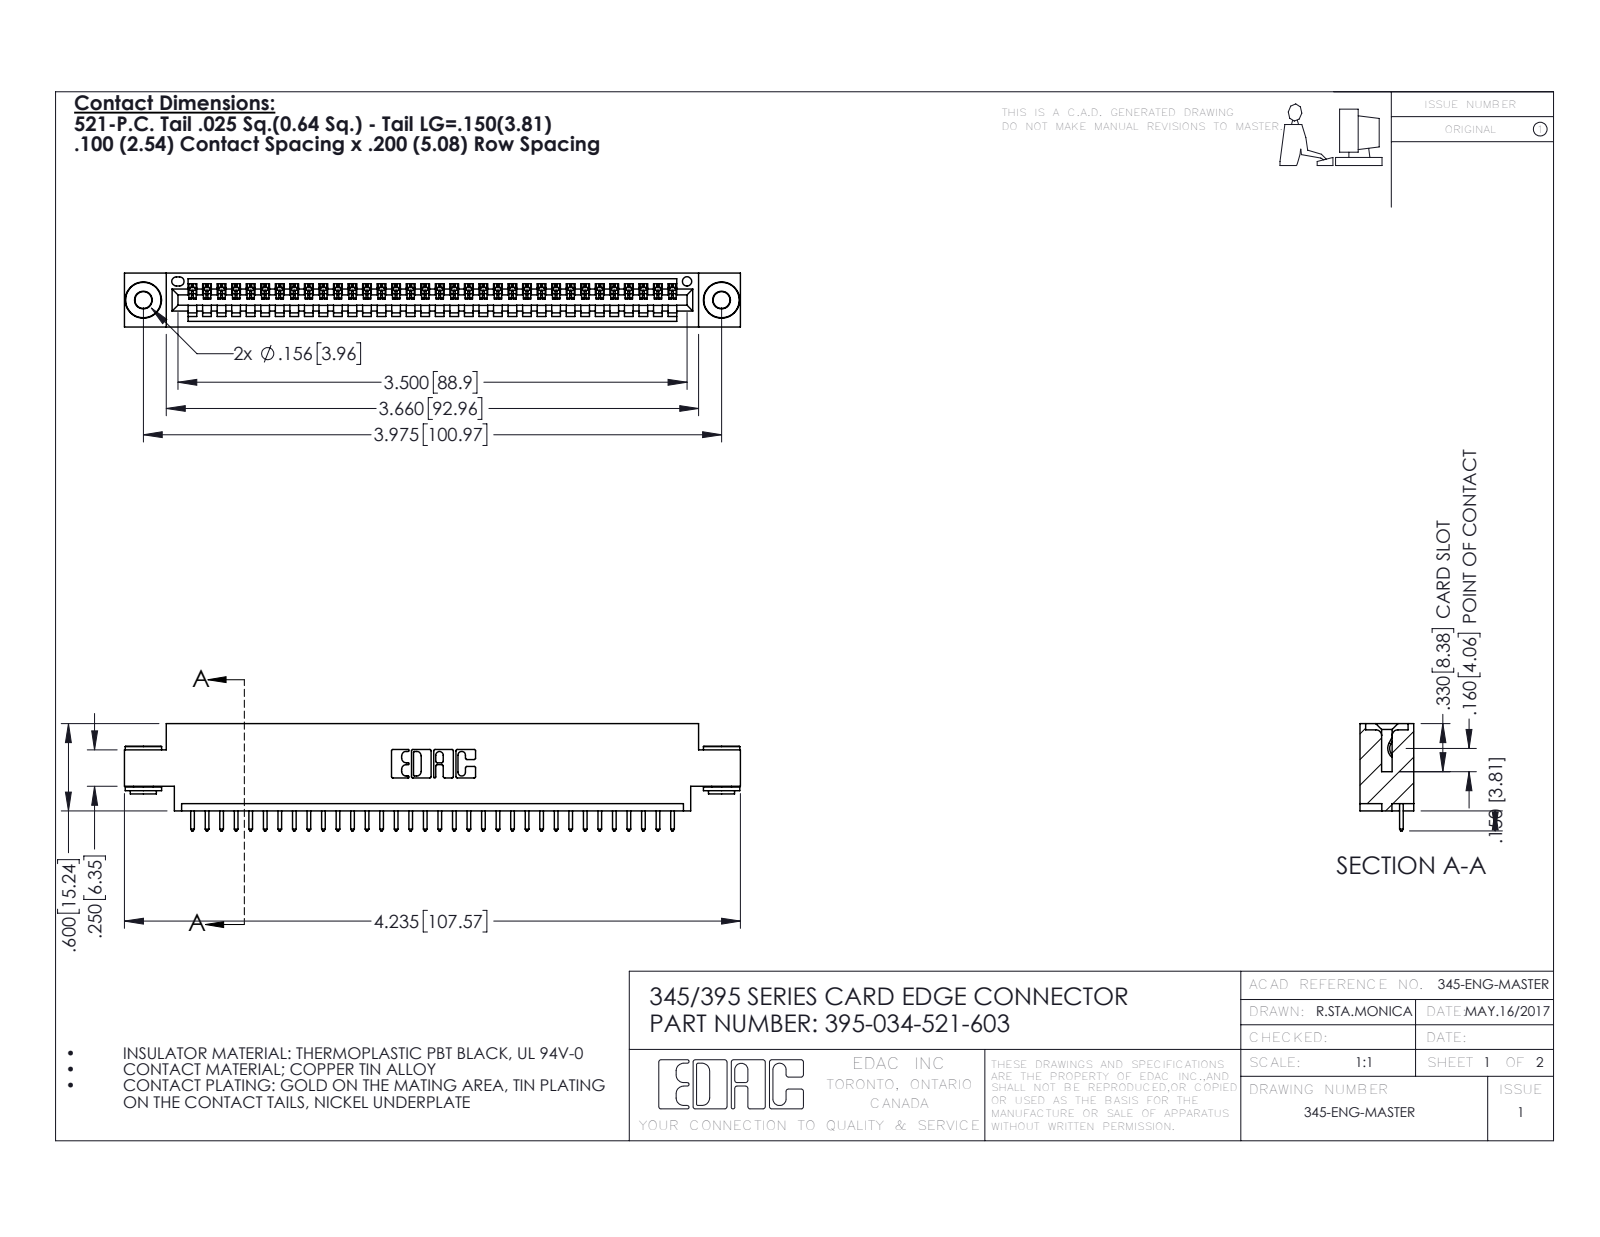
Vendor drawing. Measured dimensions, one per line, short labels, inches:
name: 345-250-002_345-250-002-102; 345-292-001_345-293-121; 395-034-521-603; 345 Part_0.170 Offset - 0.156 Dia-TH
written by: SolidWorks 2016 (CONFIG_CONTROL_DESIGN)
unit: in
bodies: 37 solids, 2140 faces (1454 planar, 678 cylindrical, 8 other)
size: 4.235 × 0.737 × 0.37
volume: 0.608 in³; area: 20.29 in²
holes: 2× ⌀0.116, 2× ⌀0.156, 1× ⌀0.064
bosses: 2× ⌀0.25, 2× ⌀0.18, 2× ⌀0.136
rounds: 68× R0.006, 68× R0.01, 22× R0.01, 6× R0.007, 6× R0.031, 3× R0.026, 2× R0.031, 2× R0.04
face distances: 0.072, 0.298, 0.37, 0.2, 0.098, 0.272, 0.025, 0.225, 0.175, 0.149
hole spacings: 0.27, 3.74, 3.975
